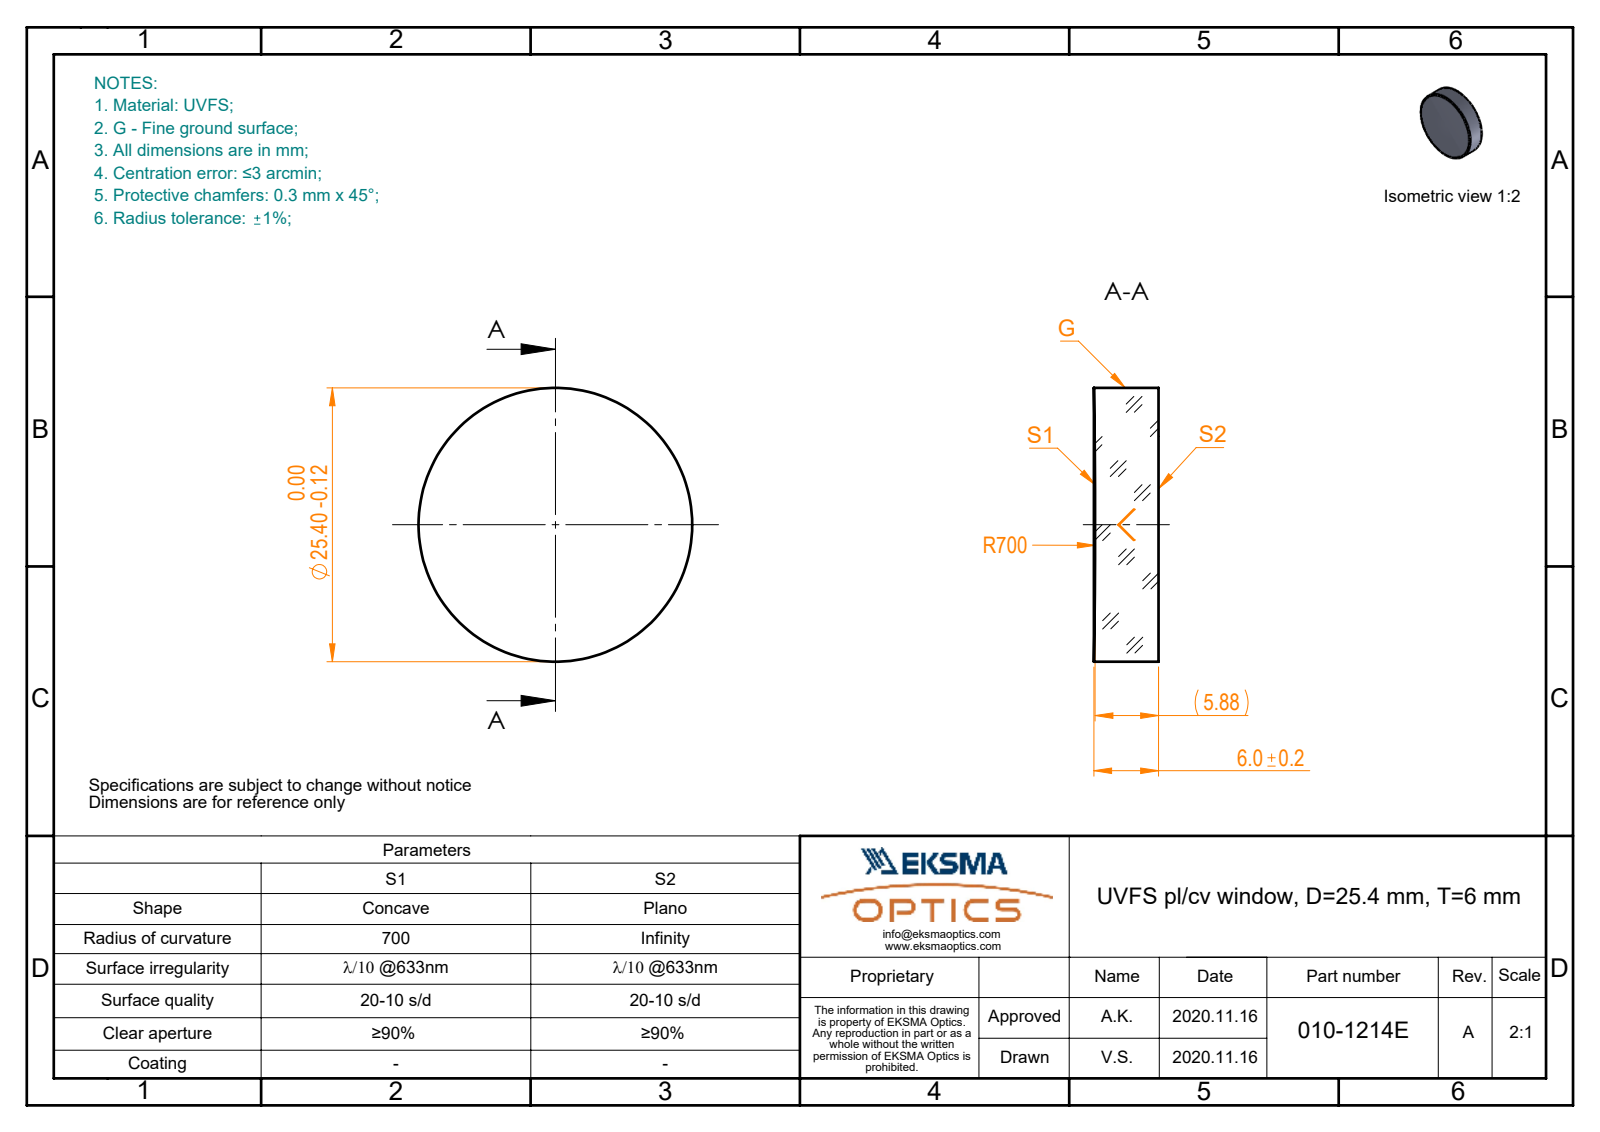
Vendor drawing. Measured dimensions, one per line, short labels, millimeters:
name: 010-1214E_UVFS_PCV_window
written by: SolidWorks 2019 (CONFIG_CONTROL_DESIGN)
unit: mm
bodies: 1 solid, 5 faces (1 planar, 2 cylindrical, 2 other)
size: 25.4 × 25.4 × 6
volume: 3 011 mm³; area: 1 492 mm²
bosses: 1× ⌀25.4
